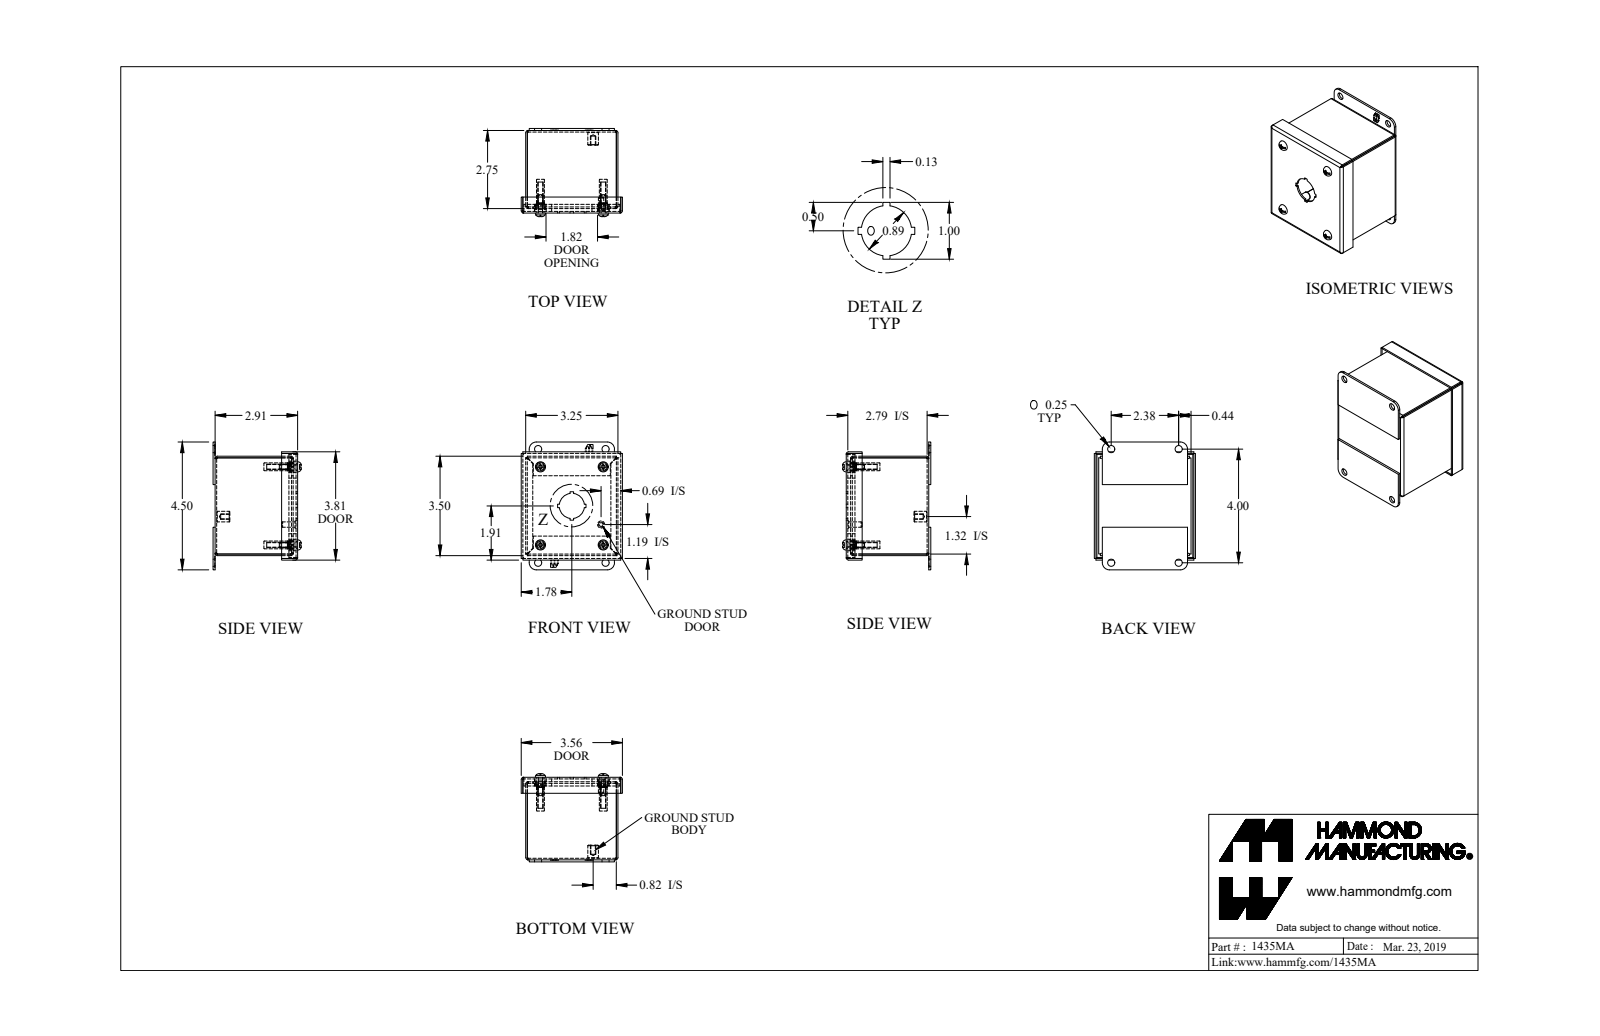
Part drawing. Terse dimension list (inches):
name: 1435MA_Default
written by: SolidWorks 2019 (CONFIG_CONTROL_DESIGN)
unit: in
bodies: 19 solids, 571 faces (371 planar, 144 cylindrical, 56 other)
size: 4.5 × 3.562 × 3.106
volume: 6.249 in³; area: 191.9 in²
holes: 8× ⌀0.25, 4× ⌀0.159, 4× ⌀0.406, 1× ⌀0.156, 1× ⌀0.886
bosses: 4× ⌀0.39, 4× ⌀0.275, 4× ⌀0.19, 4× ⌀0.148, 1× ⌀0.375, 1× ⌀0.25, 1× ⌀0.188
rounds: 12× R0.029, 12× R0.086, 4× R0.16, 4× R0.171, 4× R0.25
face distances: 0.057, 2.85, 0.057, 3.193, 3.443, 2.907, 2.793, 0.156, 2.979, 2.922
hole spacings: 2.75, 3.376, 1.765, 2.21, 2.211, 2.326, 2.376, 0.63
